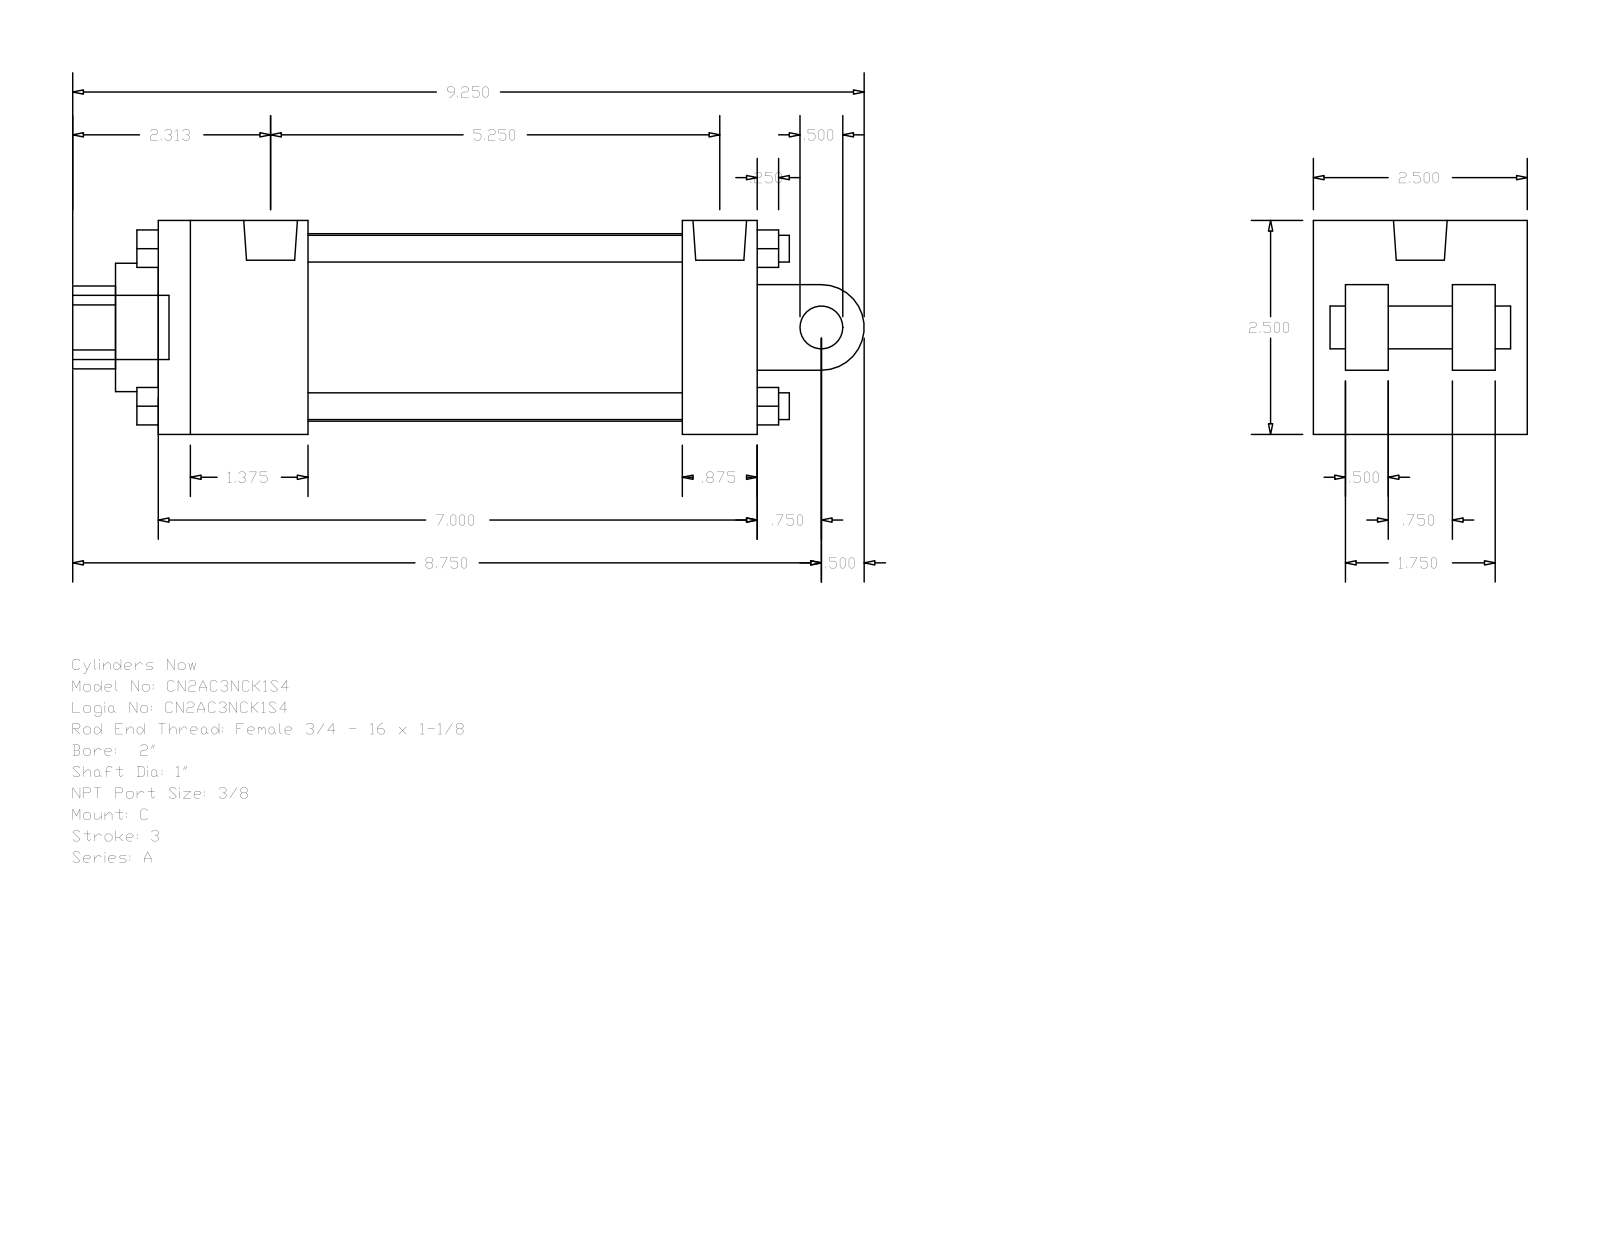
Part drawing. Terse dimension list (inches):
name: A_C__0200_1
written by: GSSL Pune (CONFIG_CONTROL_DESIGN)
unit: in
bodies: 0 solids, 135 faces (102 planar, 33 cylindrical, 0 other)
size: 9.25 × 2.5 × 2.5
holes: 2× ⌀0.219, 1× ⌀0.627, 1× ⌀1, 1× ⌀1.5, 1× ⌀2.19
bosses: 4× ⌀0.313, 2× ⌀0.219, 1× ⌀0.75, 1× ⌀0.627, 1× ⌀0.5
rounds: 1× R0.484, 1× R0.5
face distances: 2.5, 7, 1.75, 0.5, 0.375, 1.625, 5.25, 6.125, 4.375, 0.875
hole spacings: 0.157
